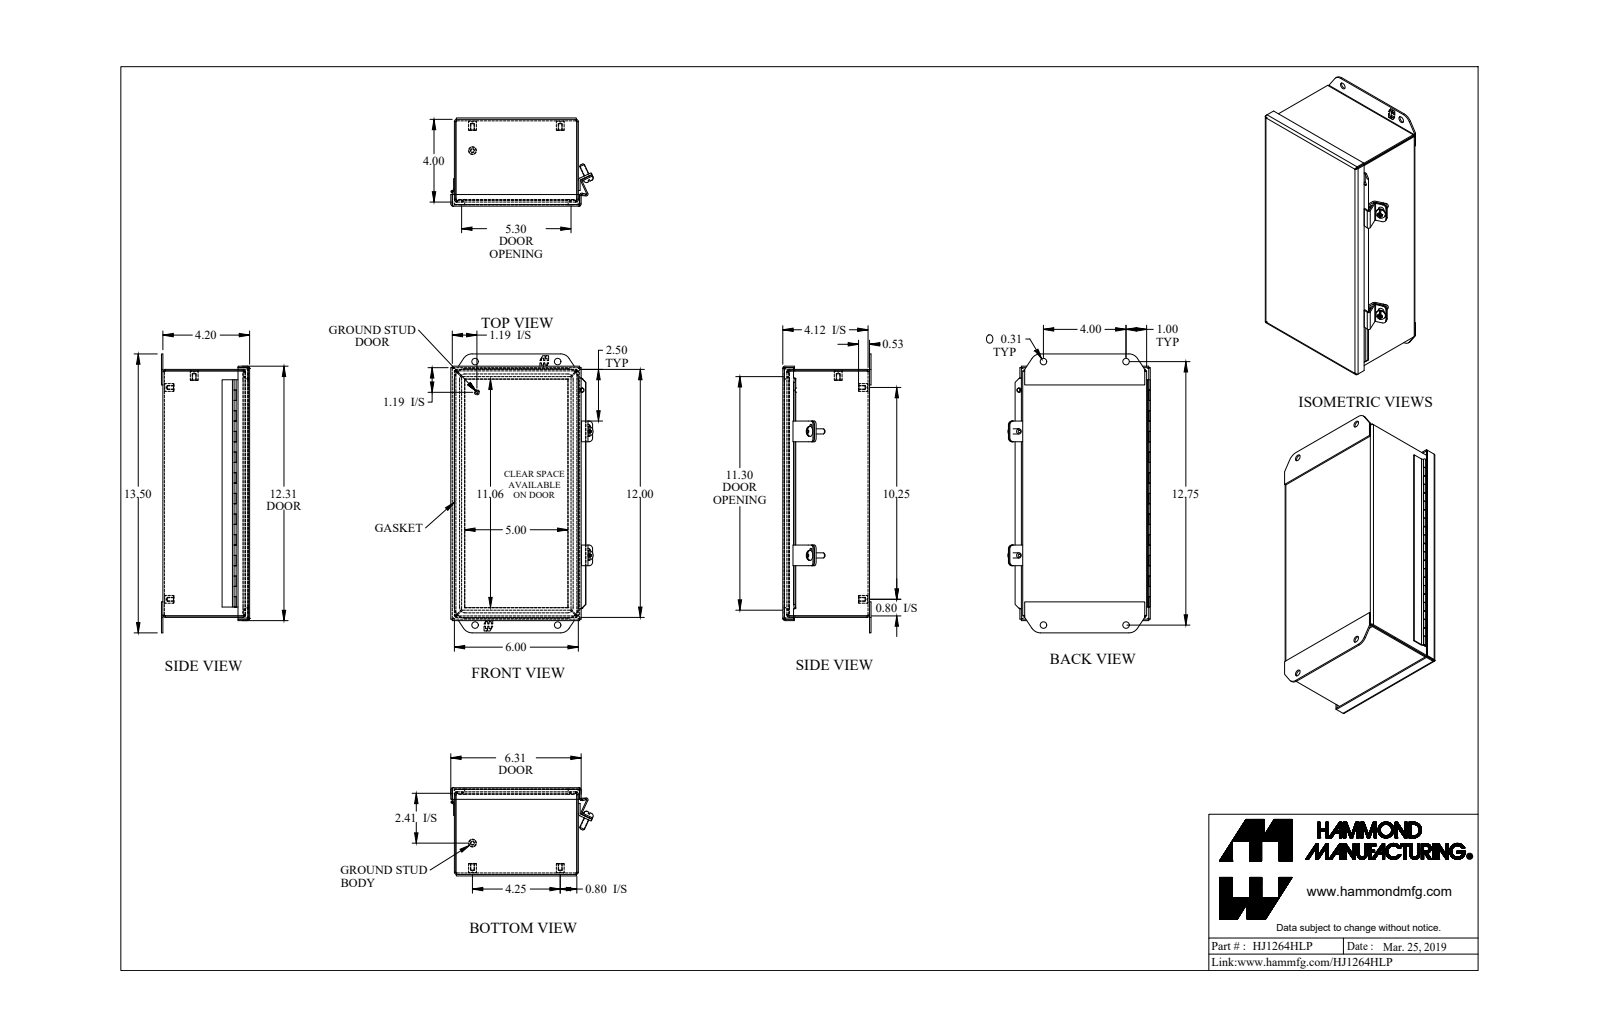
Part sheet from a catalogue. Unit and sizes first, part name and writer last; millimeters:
Units: millimetres
Overall size (bounding box): 342.9 × 175.2 × 108.4
Round holes (diameter × count): ⌀4 ×5, ⌀8 ×4, ⌀5.4 ×2, ⌀1.3 ×1
Round bosses / shafts (diameter × count): ⌀9.5 ×5, ⌀6.4 ×3, ⌀12.2 ×2, ⌀4.8 ×1, ⌀2.5 ×1, ⌀1.1 ×1
Partial cylindrical surfaces — rounded edges, fillets, slot ends (radius × count): R6.4 ×16, R0.9 ×13, R2.7 ×13, R0.3 ×4, R3.6 ×4, R4.8 ×4, R12.7 ×4, R12.7 ×4
Main face-to-face distances: 1.8, 104.8, 150.6, 106.6, 102.9, 152.4, 148.7, 303, 304.8, 301.1
Hole centre spacings: 31.9, 109.5, 292.1, 310.3, 101.6, 108, 260.4, 281.8
Volume: 466 500 mm³ · Surface area: 519 500 mm²
Bodies: 20 solids, 777 faces (414 planar, 235 cylindrical, 128 other)
Part name (STEP PRODUCT): HJ1264HLP
STEP written by: SolidWorks 2018 (AUTOMOTIVE_DESIGN)
